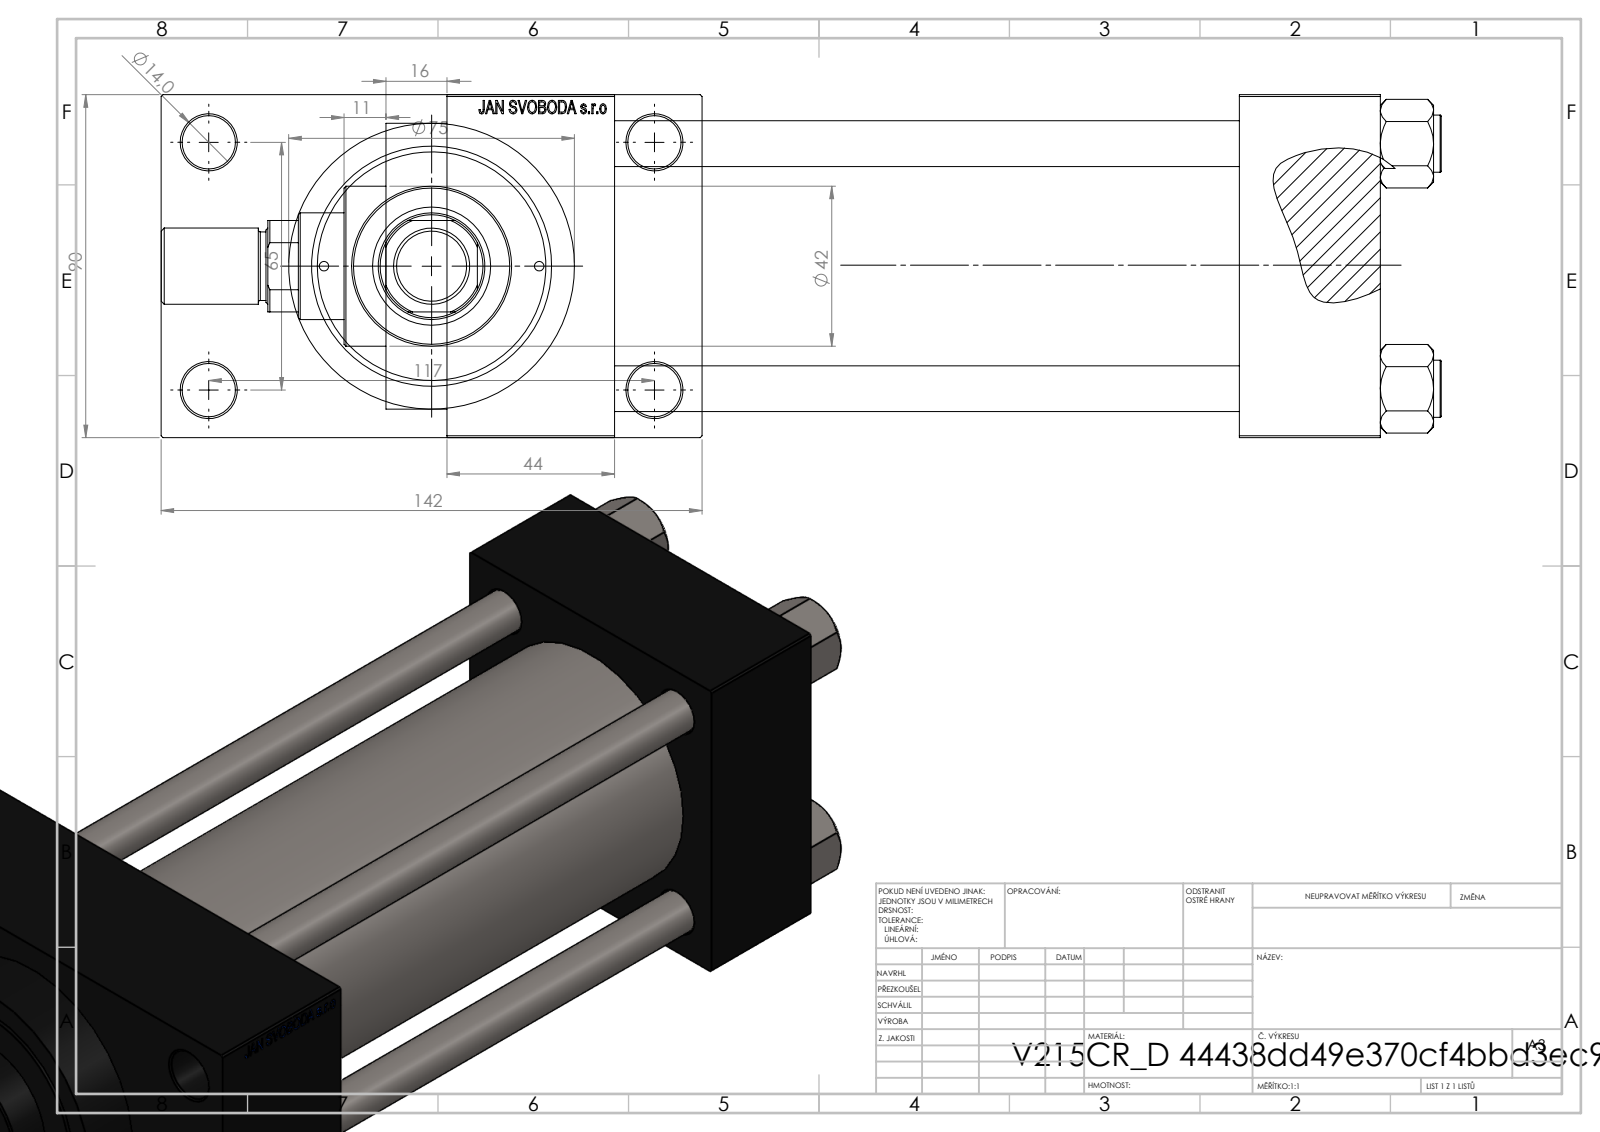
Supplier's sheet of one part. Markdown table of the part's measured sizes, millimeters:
| quantity | value |
| --- | --- |
| part name | V215_VC_A; NUT_M5_D; V215CR_VCP_D; V215CR_D_TYCINKA (+2 more) |
| STEP written by | SolidWorks 2019 (CONFIG_CONTROL_DESIGN) |
| units | millimeters |
| bodies | 12 solids, 1125 faces (503 planar, 96 cylindrical, 526 other) |
| overall size | 336 × 142 × 90 |
| volume | 1 282 000 mm³ |
| surface area | 271 275 mm² |
| round holes (diameter × count) | 12 × 4, 14 × 4, 2.5 × 2, 7 × 2, 20.96 × 2, 30 × 2, 18.5 × 1, 28 × 1, 31 × 1, 50 × 1, 60 × 1, 63 × 1 |
| round bosses / shafts (diameter × count) | 15 × 4, 75 × 1, 69 × 1, 42 × 1, 20 × 1, 18 × 1 |
| partial cylindrical surfaces (radius × count) | 13.5 × 1 |
| main face-to-face distances | 90, 164, 37, 201, 208, 245, 44, 26, 116, 16 |
| hole center spacings | 26.35, 32.39, 44.4, 45.47, 64.3, 66.92, 68.42, 69.81 |
